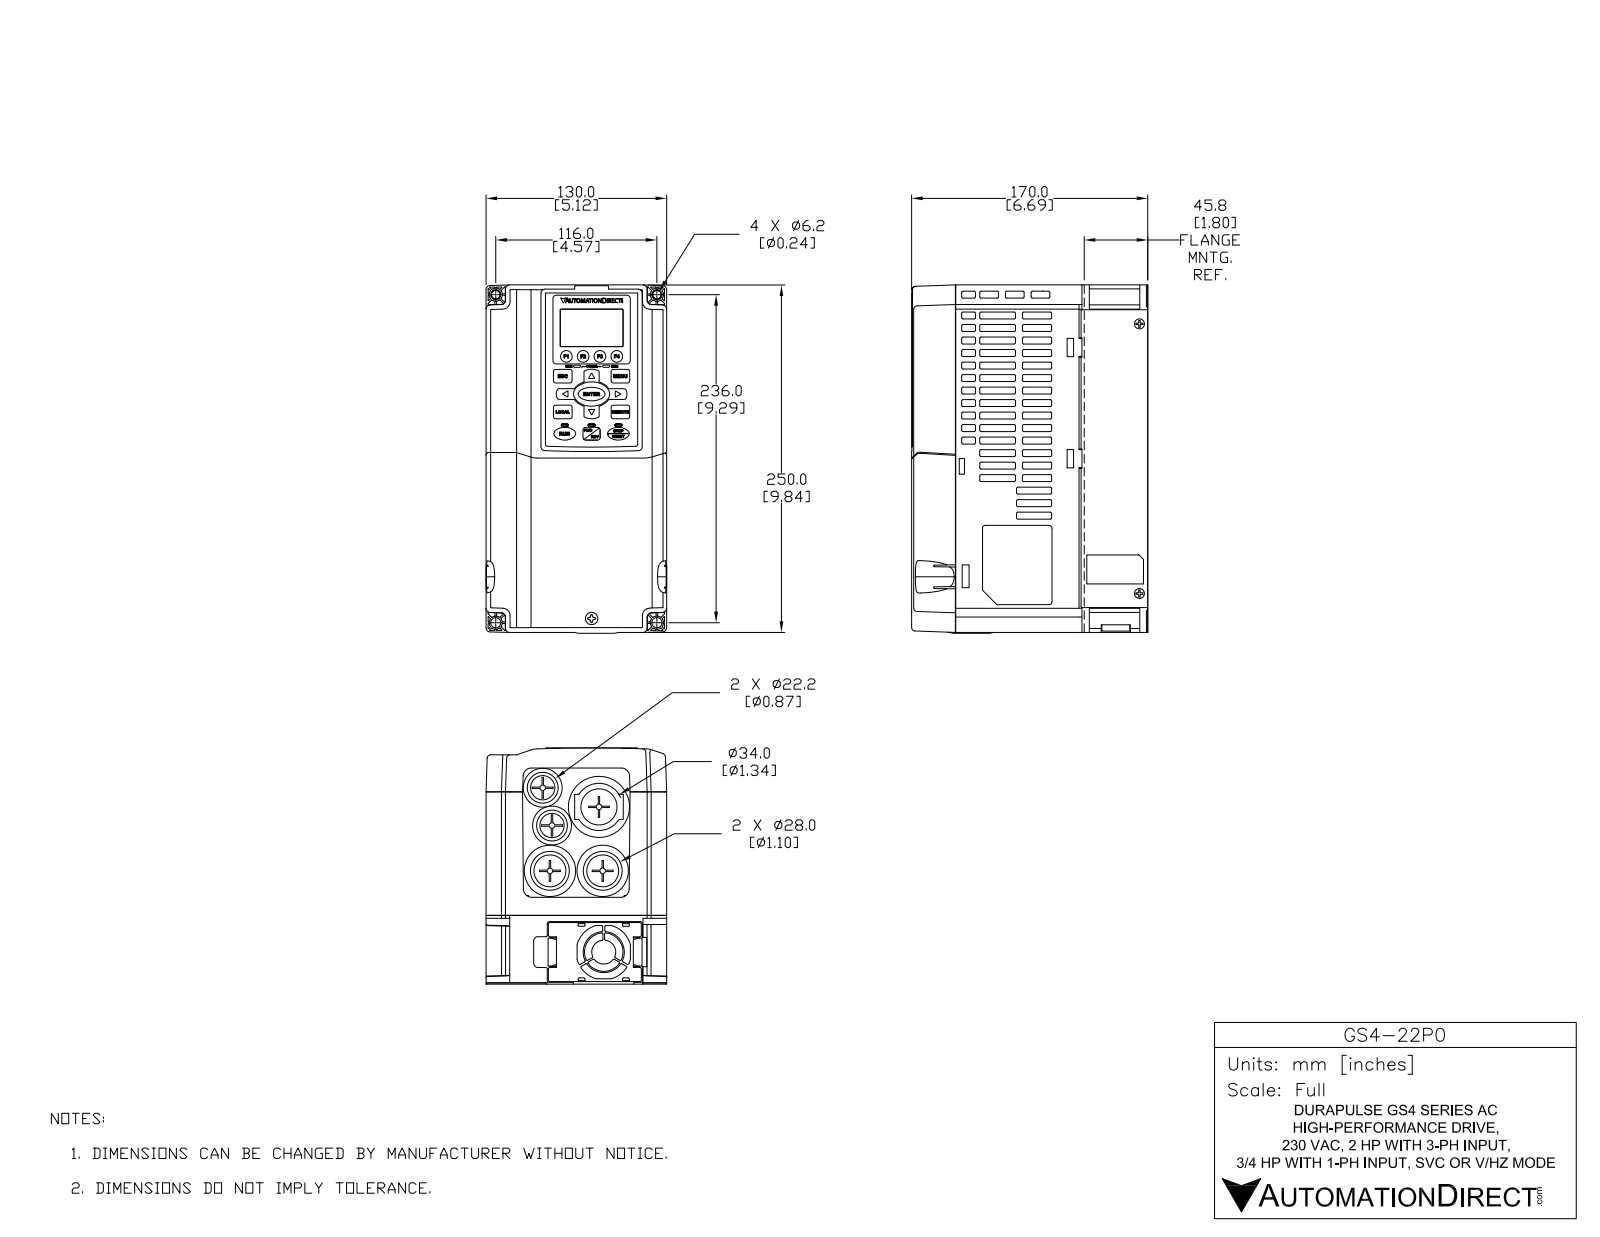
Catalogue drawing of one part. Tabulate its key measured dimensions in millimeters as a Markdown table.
| quantity | value |
| --- | --- |
| part name | GS4-PD~3 GD POS 1 Basic Red1 w UC n Lid B fxt |
| STEP written by | SolidWorks 2017 (AUTOMOTIVE_DESIGN) |
| units | millimeters |
| bodies | 23 solids, 5937 faces (3008 planar, 1800 cylindrical, 1129 other) |
| overall size | 250.7 × 170 × 131 |
| volume | 2 950 000 mm³ |
| surface area | 538 600 mm² |
| round holes (diameter × count) | 4 × 7, 3.5 × 4, 4.5 × 3, 4.4 × 2, 4.6 × 2, 6 × 2, 6.2 × 2, 7.2 × 2, 16.5 × 2, 21.5 × 2, 22.2 × 2, 28 × 2 |
| round bosses / shafts (diameter × count) | 37 × 2, 28 × 2, 27.5 × 2, 21.5 × 2, 6.8 × 2, 6 × 2, 5.4 × 2, 3.5 × 2 |
| partial cylindrical surfaces (radius × count) | 1 × 347, 0.5 × 236, 0.3 × 188, 0.2 × 170, 1.5 × 54, 2 × 53, 3 × 40, 2.5 × 20 |
| main face-to-face distances | 1, 61.1, 60.1, 133.9, 132.9, 72.8, 155.7, 154.7, 94.6, 21.8 |
| hole center spacings | 9.9, 16.1, 82, 115.6, 182.1, 217.8, 224, 233.8 |
